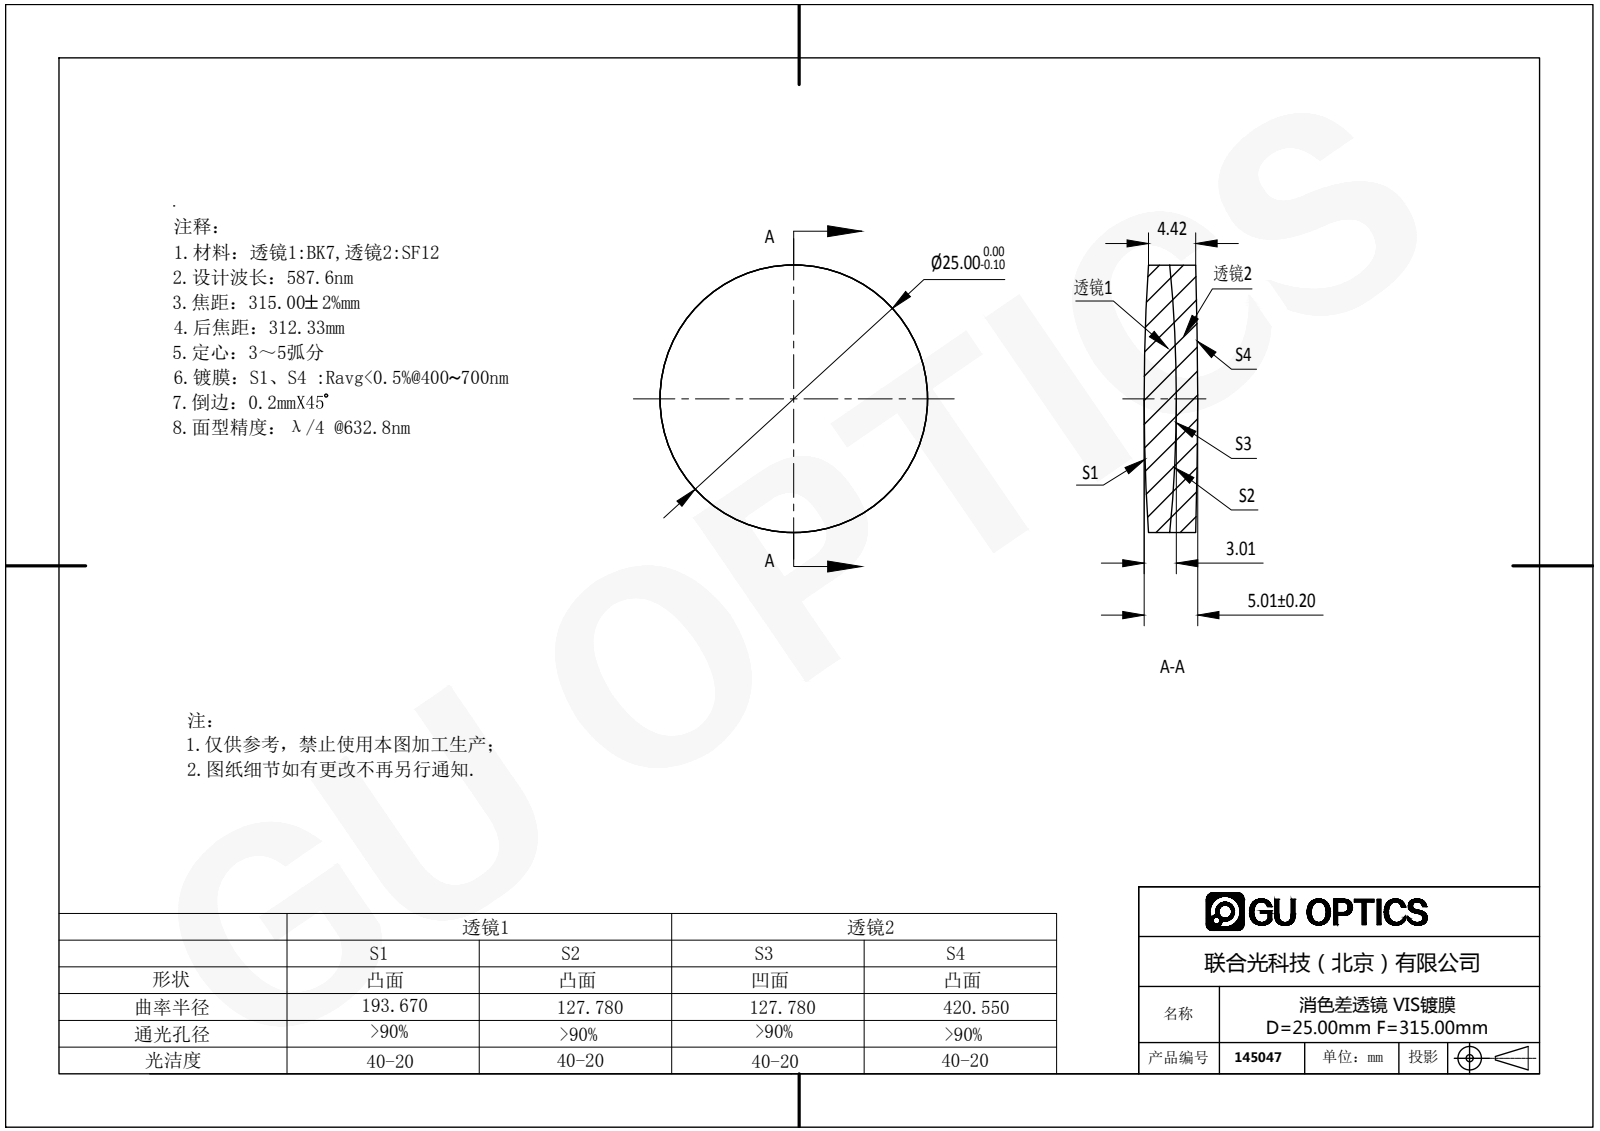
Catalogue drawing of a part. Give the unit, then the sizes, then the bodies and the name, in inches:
Units: inches
Overall size (bounding box): 0.984 × 0.984 × 0.197
Round bosses / shafts (diameter × count): ⌀0.984 ×1
Volume: 0.141 in³ · Surface area: 3.587 in²
Bodies: 2 solids, 12 faces (0 planar, 4 cylindrical, 8 other)
Part name (STEP PRODUCT): 145047
STEP written by: SolidWorks 2016 (AUTOMOTIVE_DESIGN)
